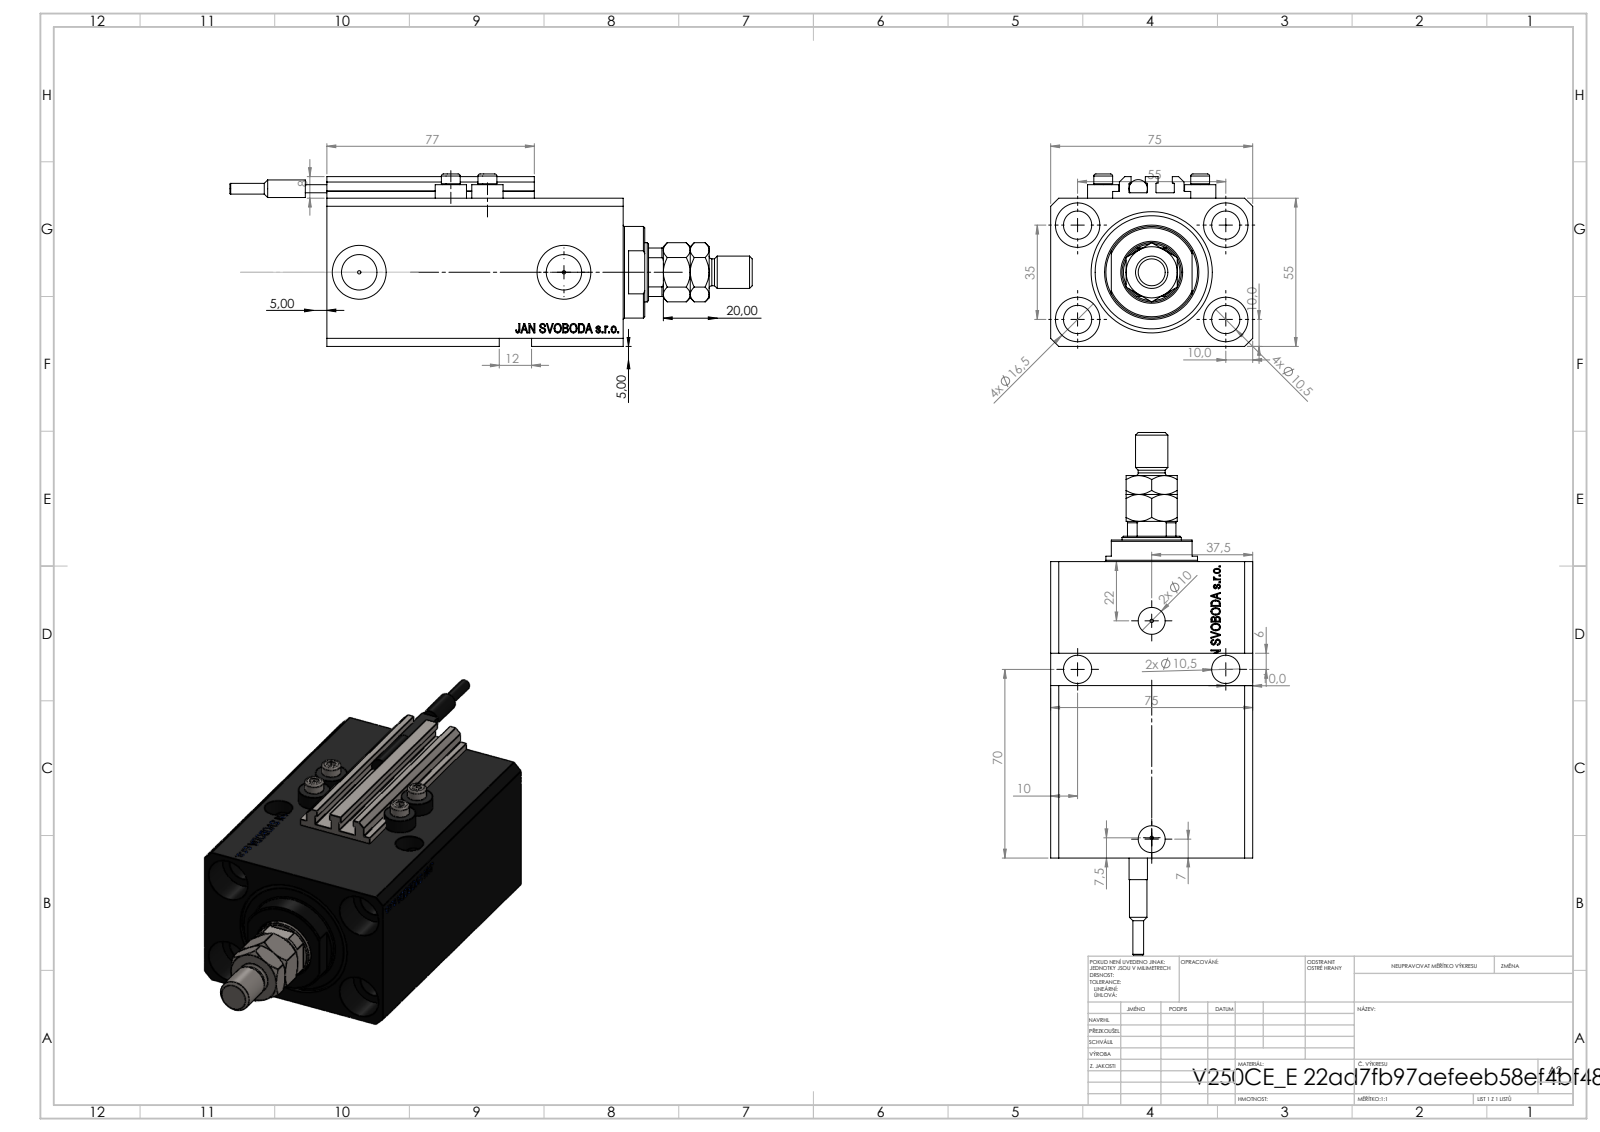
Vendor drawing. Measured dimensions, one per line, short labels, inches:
name: V250CE_C_VCP; SWITCH_V250CE; MTA; V250CE_E_Body (+2 more)
written by: SolidWorks 2019 (CONFIG_CONTROL_DESIGN)
unit: in
bodies: 10 solids, 1159 faces (545 planar, 156 cylindrical, 458 other)
size: 7.638 × 2.953 × 2.52
volume: 23.81 in³; area: 154 in²
holes: 9× ⌀0.413, 4× ⌀0.049, 4× ⌀0.157, 4× ⌀0.65, 2× ⌀0.394, 2× ⌀0.518, 2× ⌀0.787, 1× ⌀0.866, 1× ⌀1.26, 1× ⌀1.772
bosses: 4× ⌀0.457, 4× ⌀0.276, 1× ⌀1.339, 1× ⌀0.472, 1× ⌀0.394, 1× ⌀0.268, 1× ⌀0.256, 1× ⌀0.157
rounds: 10× R0.008, 1× R0.413
face distances: 2.165, 2.953, 0.591, 0.118, 4.331, 3.74, 0.39, 2.244, 3.35, 3.941
hole spacings: 1.283, 1.294, 2.165, 2.706, 0.535, 0.555, 0.907, 1.016
